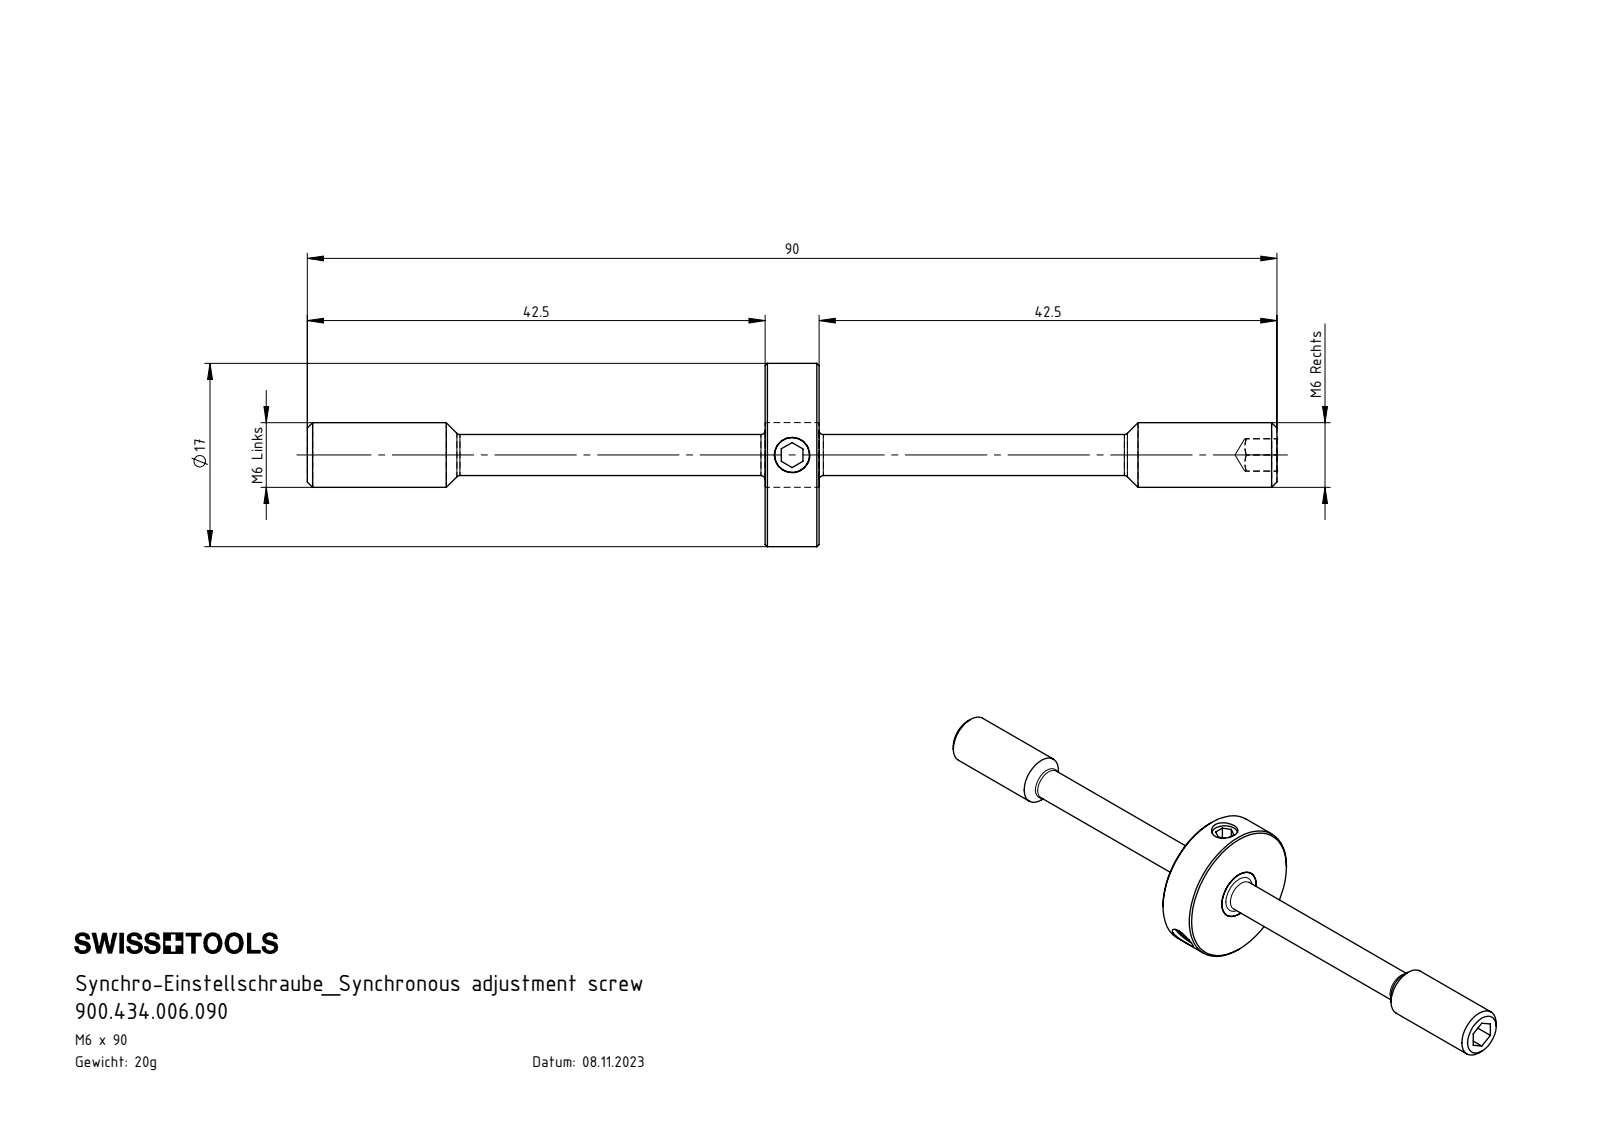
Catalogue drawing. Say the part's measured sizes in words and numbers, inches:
The part is named "Z42-ER3.002.005_A; 900.434.006.090; Z94-ER3.001.090_A; ISO 4026 - M4 x 5". Its 3-D file was written by "SolidWorks 2022 (AUTOMOTIVE_DESIGN)". It is 5 solids with 99 faces: 39 planar, 26 cylindrical and 34 other. Overall it measures 3.543 by 0.669 by 0.669 inches. Its volume is 0.154 cubic inches and its surface area 3.993 square inches. Round holes: 3 of diameter 0.13. Round bosses or shafts: 3 of diameter 0.157, 1 of diameter 0.669, 1 of diameter 0.236, 1 of diameter 0.15. The main face-to-face distances are 0.197, 1.673, 1.87, 0.079, 0.098, 0.118, 3.543, 1.732, 1.811, 0.059.
